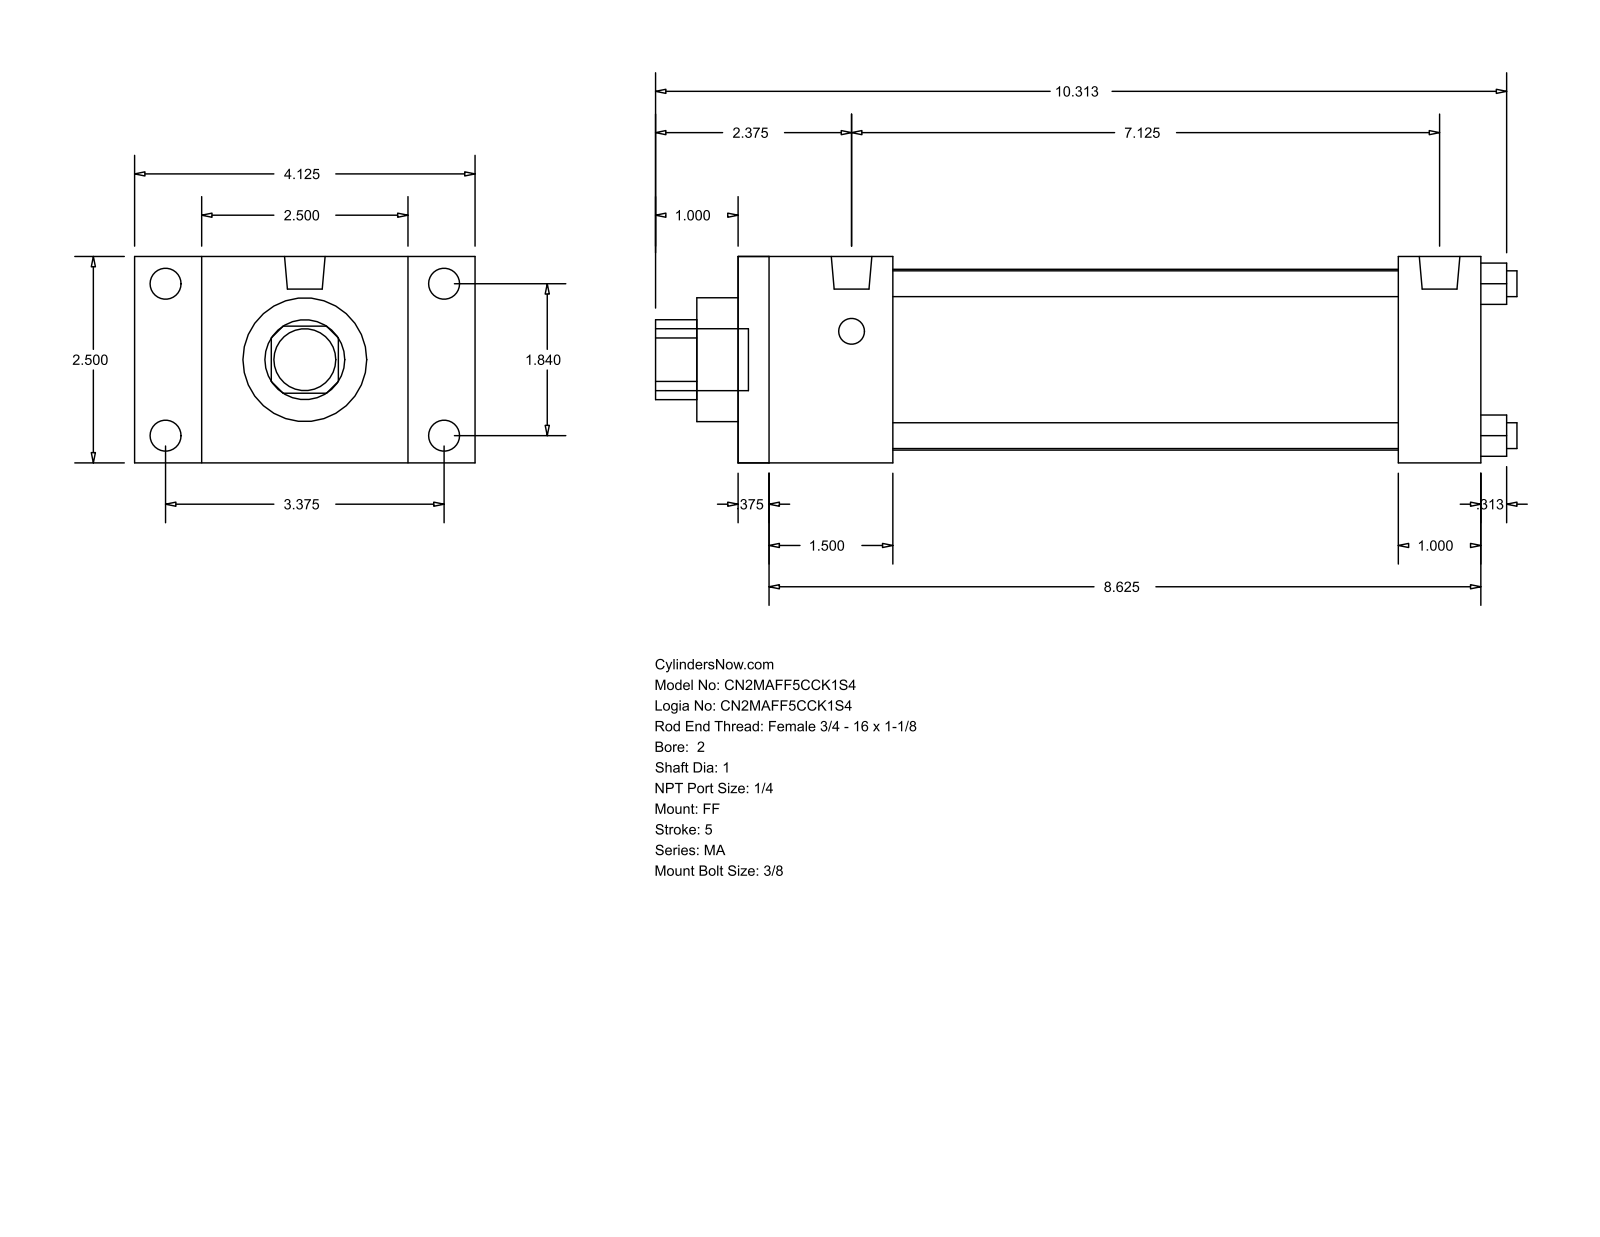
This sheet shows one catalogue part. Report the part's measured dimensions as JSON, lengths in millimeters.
{"part_name": "MA_FF__0200_1", "step_written_by": "GSSL Pune (CONFIG_CONTROL_DESIGN)", "units": "millimeters", "bodies": {"solids": 0, "faces": 92, "planar": 64, "cylindrical": 28, "other": 0}, "overall_size": [265.11, 104.78, 63.5], "round_holes": [[7.94, 4], [25.4, 1], [38.1, 1], [55.63, 1]], "round_bosses_or_shafts": [[9.53, 4], [7.94, 4], [12.49, 2], [19.05, 1]], "partial_cylinders_radius": [[12.29, 1]], "face_to_face_distances": [63.5, 228.6, 9.52, 219.08, 25.4, 20.64, 12.7, 47.63, 203.2, 38.11], "hole_center_spacings": [33.05, 46.74, 66.1]}
